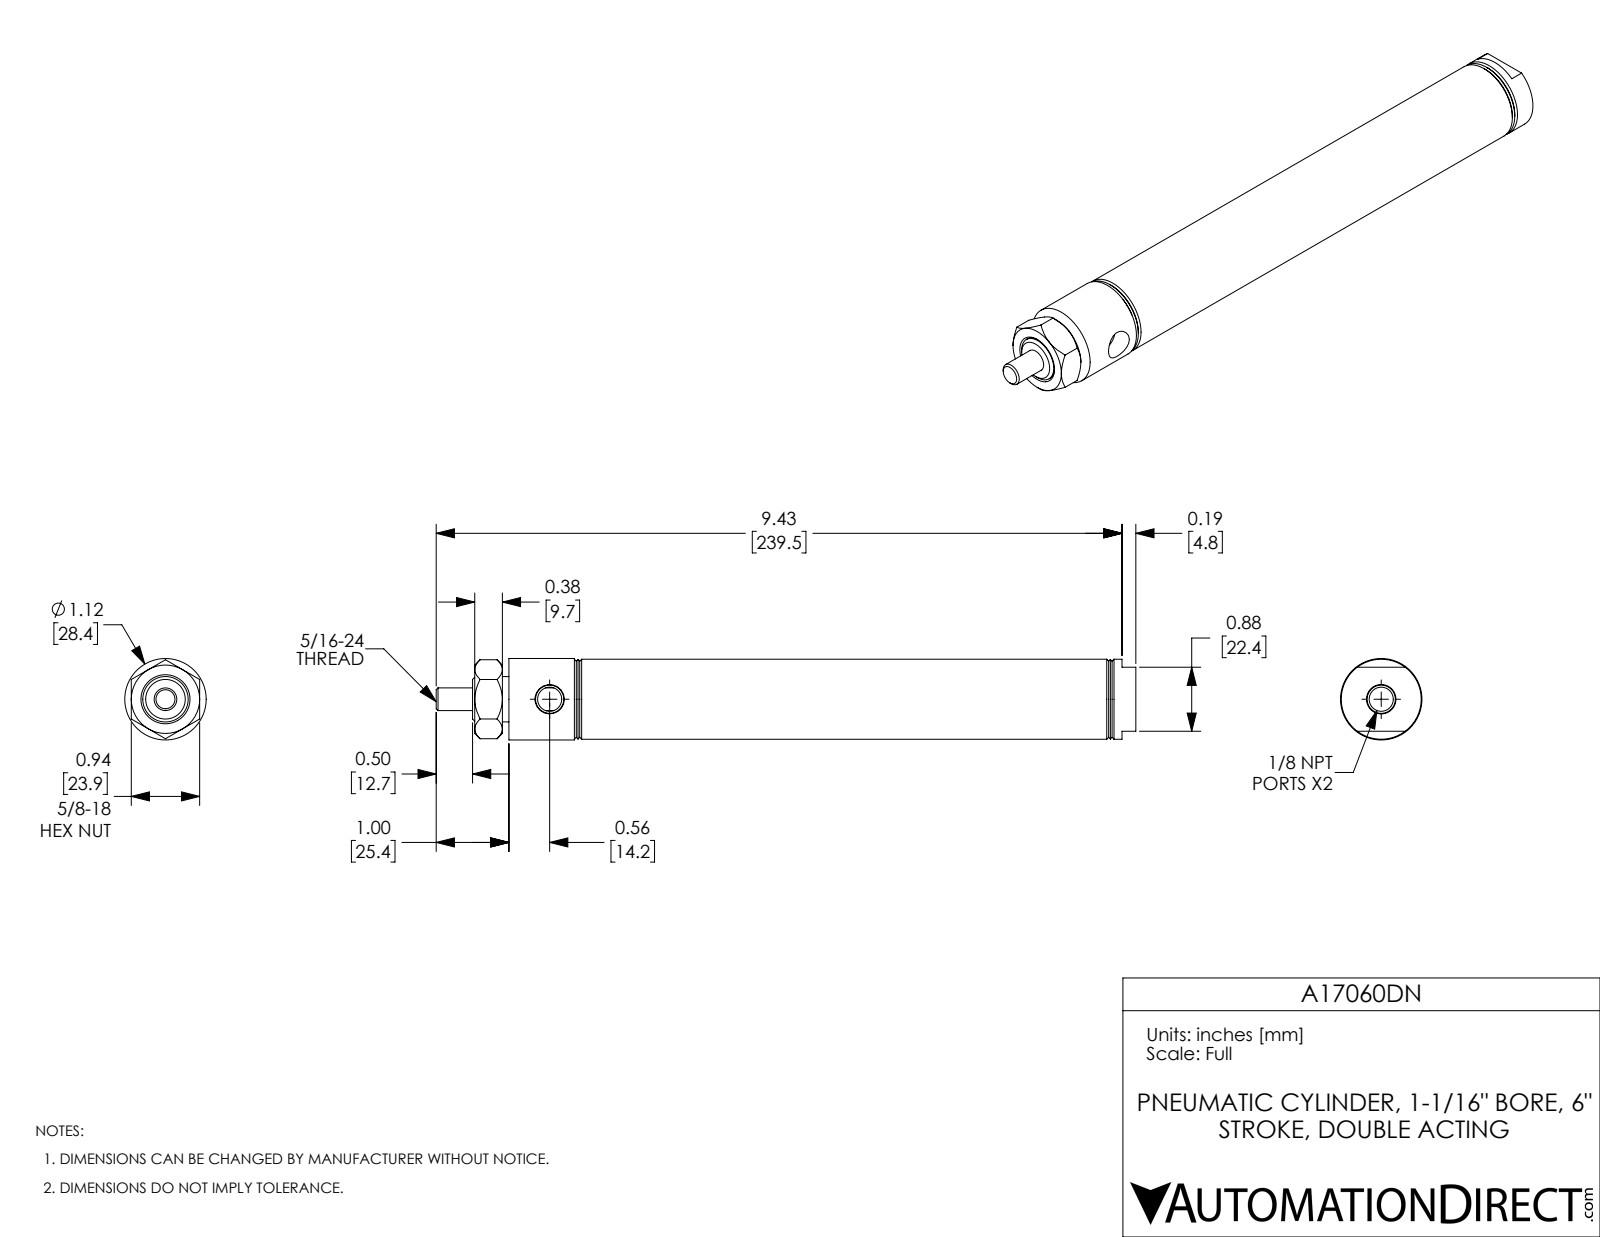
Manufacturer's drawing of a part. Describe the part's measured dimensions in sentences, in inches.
The part is named "A17060DN-Rod; A17060DN-MainBody; A17060DN; A17060DN_Mounting Nut_D-9". Its 3-D file was written by "SolidWorks 2017 (AUTOMOTIVE_DESIGN)". It is 3 solids with 94 faces: 24 planar, 26 cylindrical and 44 other. Overall it measures 9.62 by 1.12 by 1.12 inches. Its volume is 3.561 cubic inches and its surface area 73.16 square inches. Round holes: 2 of diameter 0.332, 1 of diameter 0.312, 1 of diameter 0.625, 1 of diameter 1.063. Round bosses or shafts: 1 of diameter 1.12, 1 of diameter 1.1, 1 of diameter 0.623. The main face-to-face distances are 0.5, 7.56, 6.5, 6, 1.06, 1.56, 7.56, 8.62, 7.06, 1.06.
